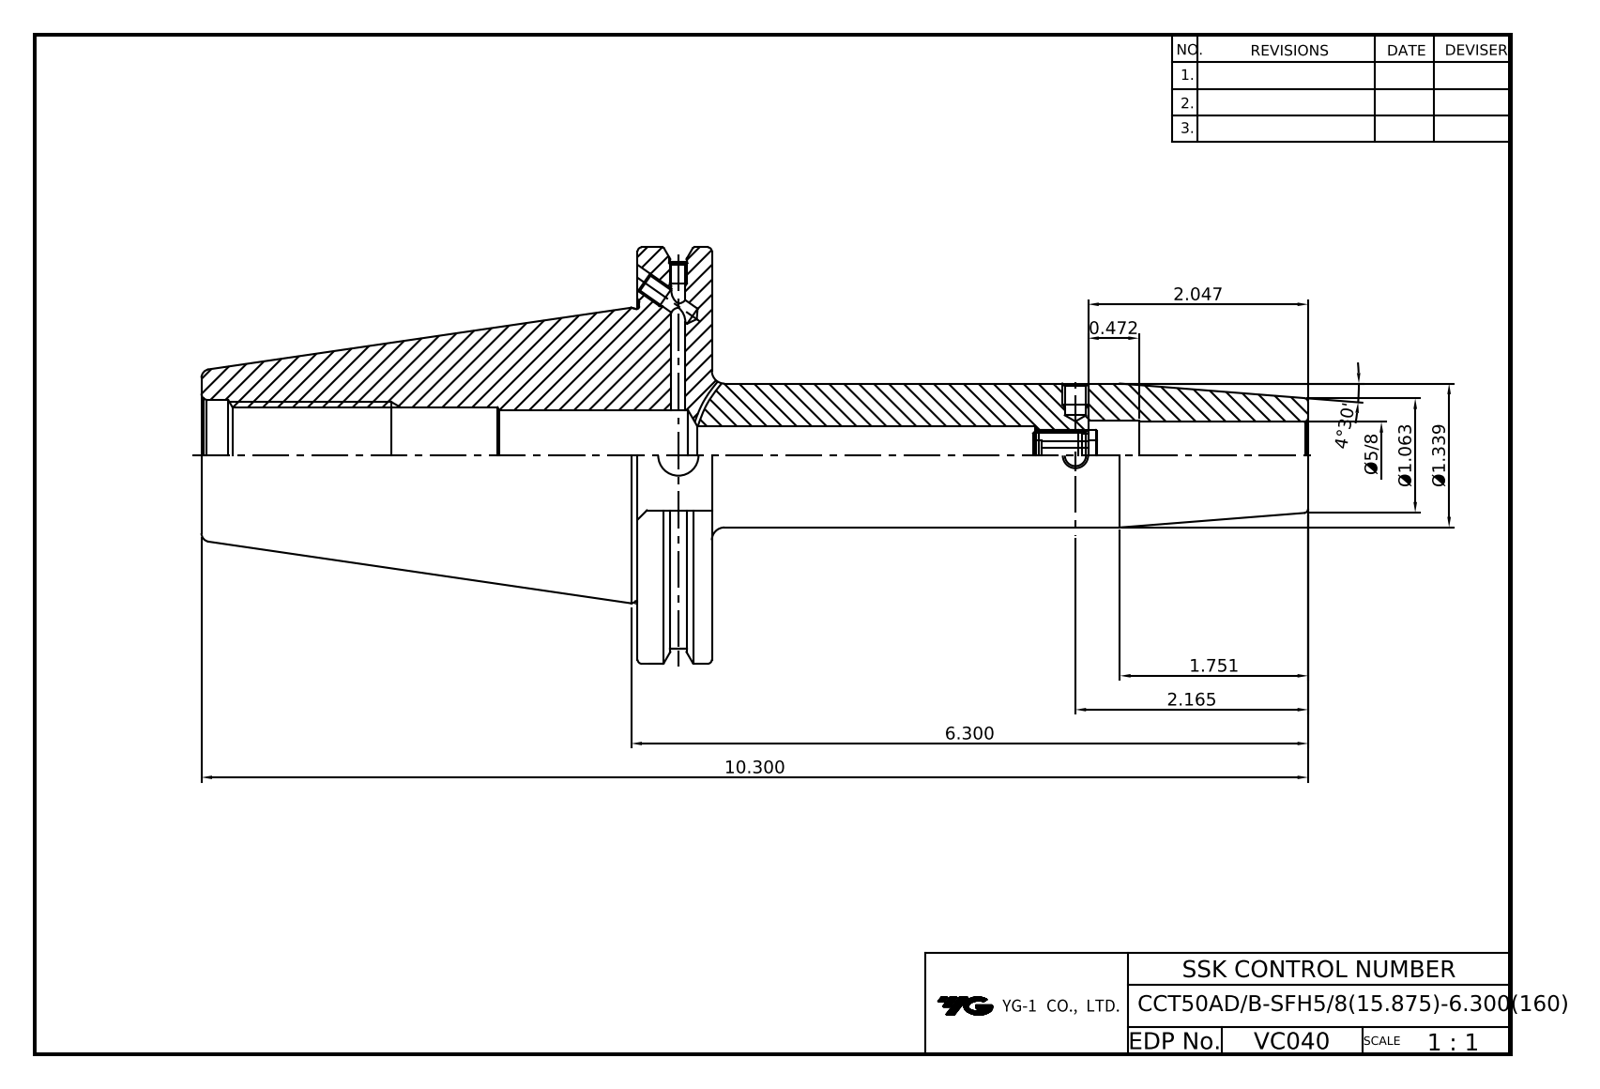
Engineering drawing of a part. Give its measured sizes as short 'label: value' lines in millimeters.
name: CCT50ADB_SFH15_875-160
written by: PRO/ENGINEER BY PARAMETRIC TECHNOLOGY CORPORATION, 2016360 (CONFIG_CONTROL_DESIGN)
unit: mm
bodies: 1 solid, 132 faces (35 planar, 54 cylindrical, 43 other)
size: 261.6 × 98.42 × 94.96
volume: 418 870 mm³; area: 70 707 mm²
holes: 6× ⌀5, 3× ⌀4.2, 1× ⌀6, 1× ⌀9.53, 1× ⌀11, 1× ⌀12, 1× ⌀14, 1× ⌀15.88, 1× ⌀16.48, 1× ⌀21.5, 1× ⌀22.8, 1× ⌀25.4
bosses: 1× ⌀98.42, 1× ⌀91.29, 1× ⌀69.25, 1× ⌀34
face distances: 17.55, 103.1, 120.65, 73.03, 25.9, 261.6, 158.5, 140.95, 103.5, 0.4
hole spacings: 93.87
